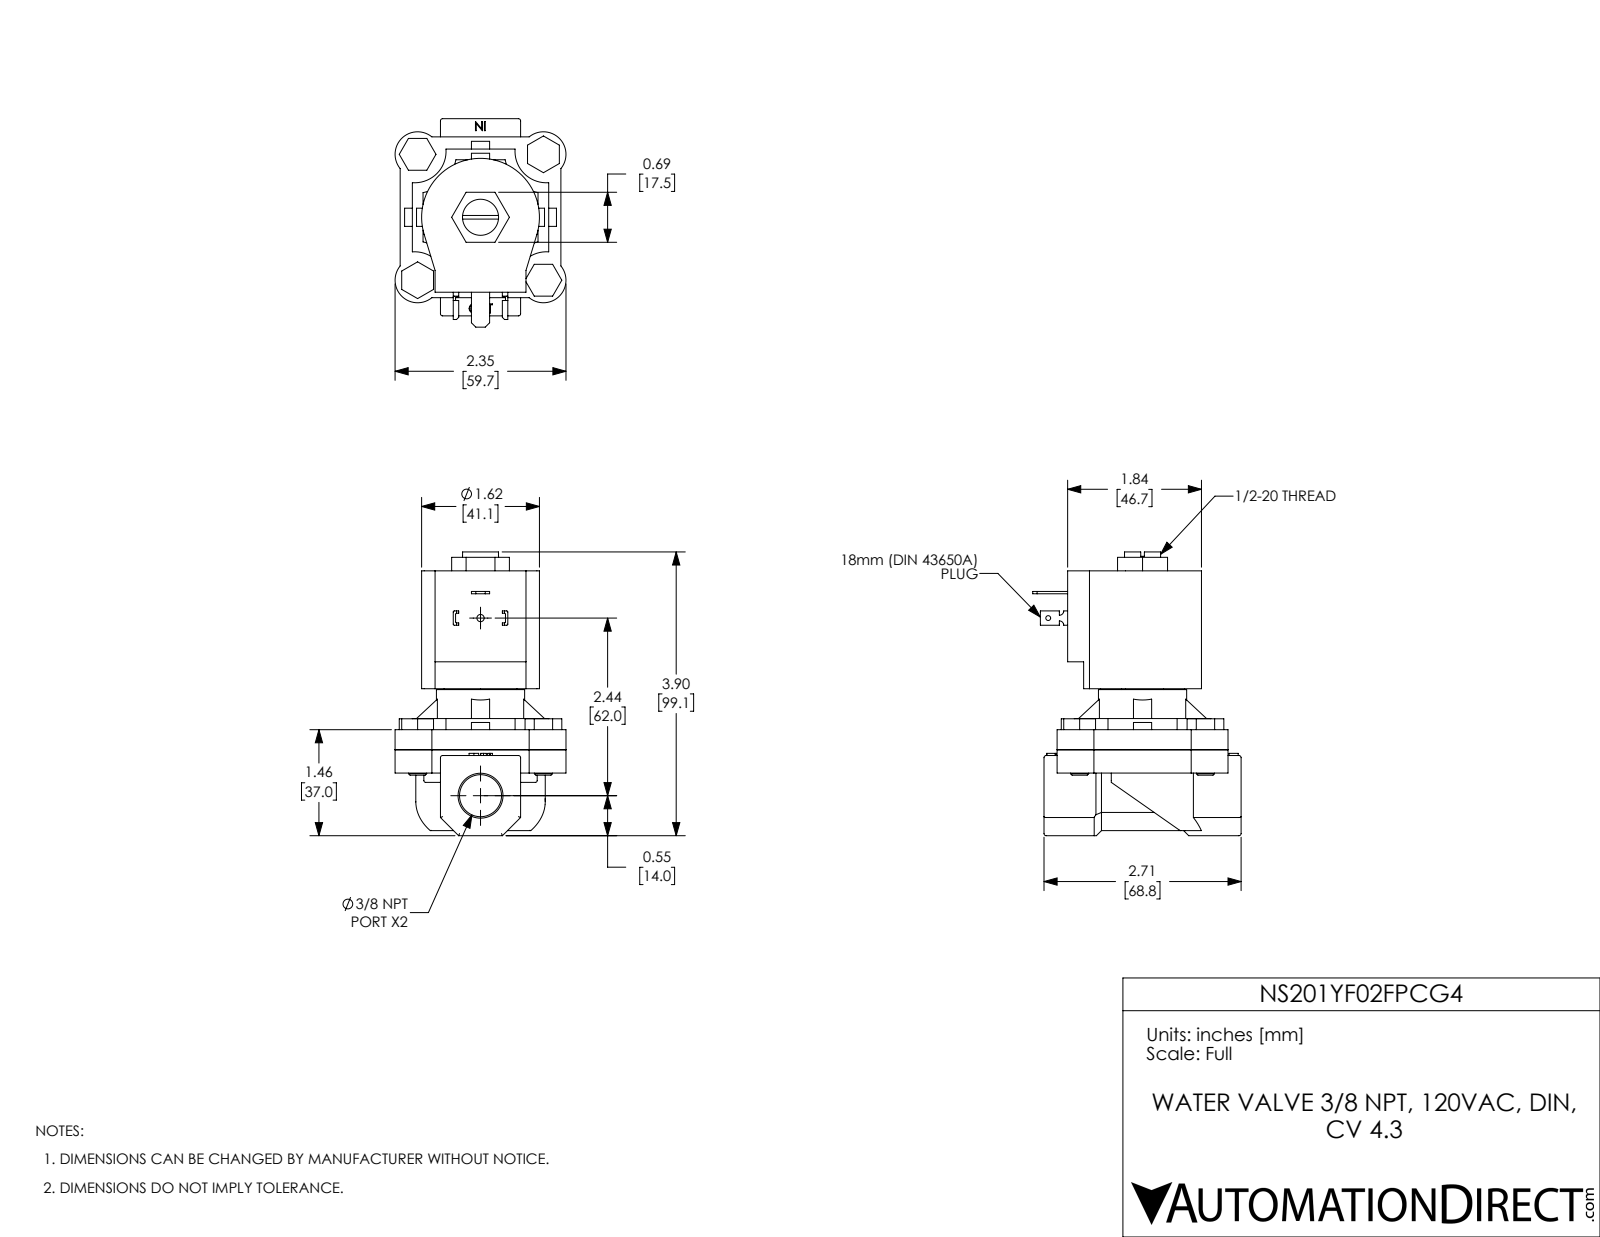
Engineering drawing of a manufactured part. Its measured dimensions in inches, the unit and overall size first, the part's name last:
Units: inches
Overall size (bounding box): 3.9 × 2.865 × 2.35
Round holes (diameter × count): ⌀0.25 ×4, ⌀0.067 ×1, ⌀0.1 ×1, ⌀0.496 ×1, ⌀0.512 ×1, ⌀0.578 ×1, ⌀1.155 ×1
Round bosses / shafts (diameter × count): ⌀0.248 ×4, ⌀1.213 ×1
Partial cylindrical surfaces — rounded edges, fillets, slot ends (radius × count): R0.03 ×15, R0.015 ×8, R0.31 ×4, R0.432 ×4, R0.579 ×4, R0.06 ×2, R0.81 ×1, R0.89 ×1
Main face-to-face distances: 0.276, 2.459, 2.183, 0.32, 0.596, 2.779, 0.554, 1.656, 0.25, 1.102
Hole centre spacings: 1.223, 1.73, 2.446, 2.441
Volume: 10.27 in³ · Surface area: 66.55 in²
Bodies: 11 solids, 383 faces (237 planar, 113 cylindrical, 33 other)
Part name (STEP PRODUCT): NS201YF02FPCG4
STEP written by: SolidWorks 2017 (AUTOMOTIVE_DESIGN)
